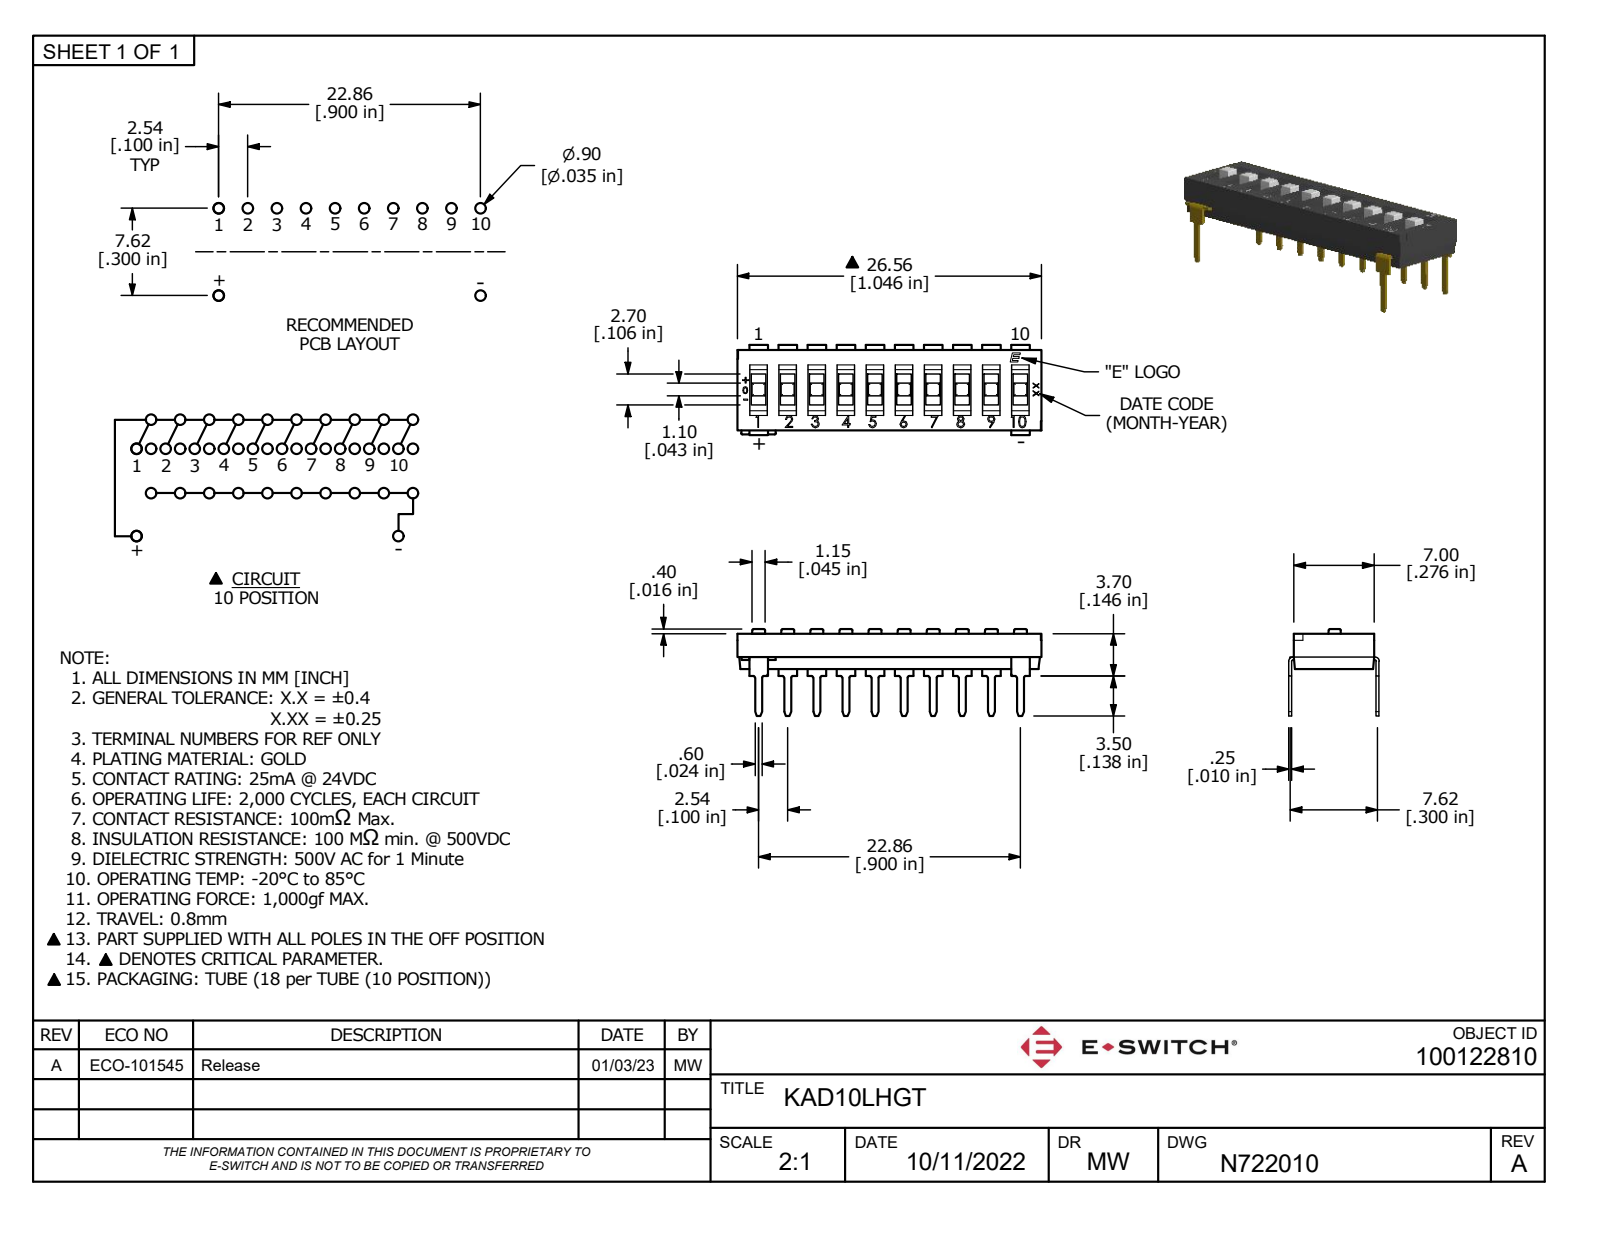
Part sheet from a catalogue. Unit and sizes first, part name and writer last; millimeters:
Units: millimetres
Overall size (bounding box): 26.56 × 7.87 × 7.6
Partial cylindrical surfaces — rounded edges, fillets, slot ends (radius × count): R0.1 ×28, R0.15 ×22, R0.35 ×2
Main face-to-face distances: 3.1, 0.44, 7, 7.19, 7.44, 7.62, 2.54, 2.69, 5.08, 0.41
Volume: 563 mm³ · Surface area: 841 mm²
Bodies: 1 solid, 689 faces (508 planar, 92 cylindrical, 89 other)
Part name (STEP PRODUCT): KAD10LHGT
STEP written by: Autodesk Inventor 2022 (AUTOMOTIVE_DESIGN)
